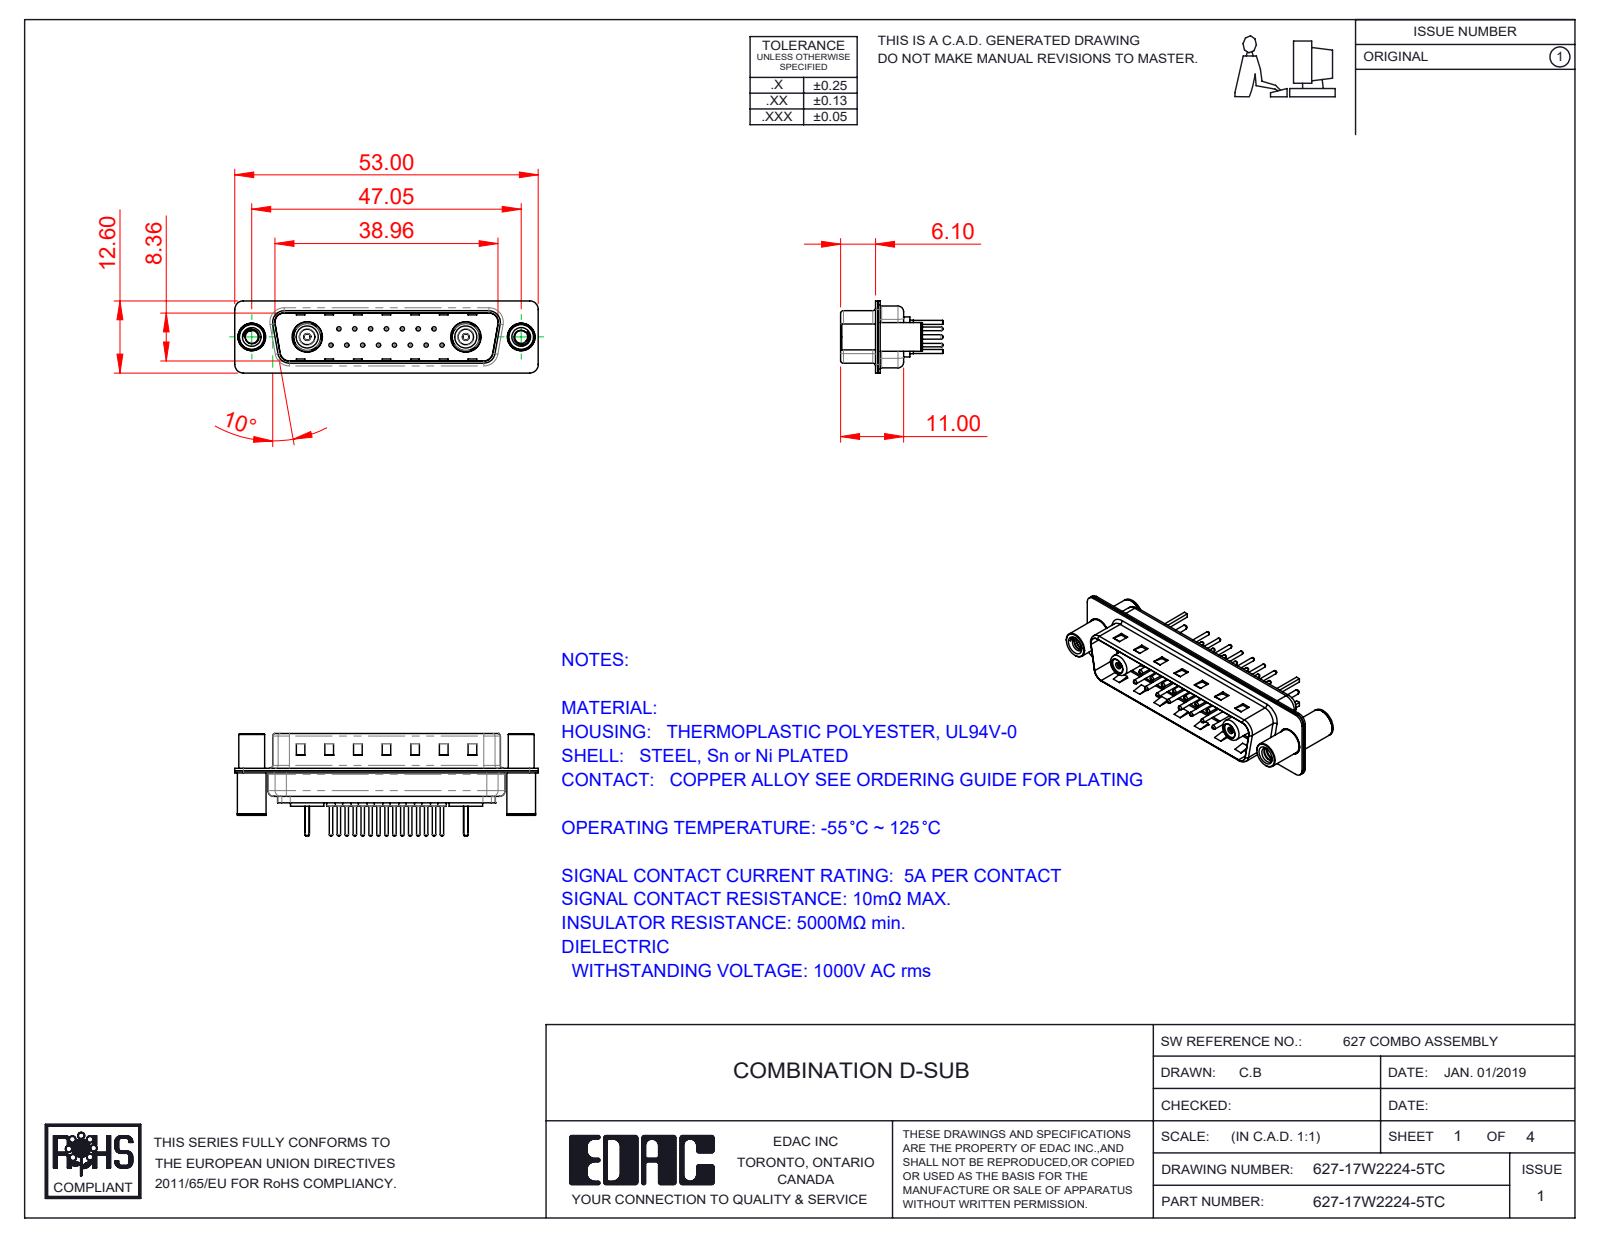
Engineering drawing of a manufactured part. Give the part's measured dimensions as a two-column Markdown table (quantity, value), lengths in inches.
| quantity | value |
| --- | --- |
| part name | 627-17W2224-5TC; Locking Collar; 627Combo Contact Row 2_24; Co-Ax Jack Assy_S (+8 more) |
| STEP written by | SolidWorks 2016 (CONFIG_CONTROL_DESIGN) |
| units | inches |
| bodies | 30 solids, 1248 faces (376 planar, 503 cylindrical, 369 other) |
| overall size | 2.087 × 0.705 × 0.496 |
| volume | 0.186 in³ |
| surface area | 12.59 in² |
| round holes (diameter × count) | 0.063 × 17, 0.03 × 15, 0.079 × 15, 0.043 × 2, 0.047 × 2, 0.059 × 2, 0.089 × 2, 0.098 × 2, 0.106 × 2, 0.128 × 2, 0.134 × 2, 0.157 × 2 |
| round bosses / shafts (diameter × count) | 0.059 × 15, 0.024 × 15, 0.23 × 2, 0.205 × 2, 0.197 × 2, 0.193 × 2, 0.189 × 2, 0.186 × 2 |
| partial cylindrical surfaces (radius × count) | 0.059 × 16, 0.079 × 12, 0.02 × 8, 0.063 × 8, 0.01 × 4, 0.024 × 4, 0.026 × 4, 0.035 × 4 |
| main face-to-face distances | 0.016, 0.032, 0.377, 0.345, 0.236, 0.059, 0.031, 0.22, 0.048, 0.393 |
| hole center spacings | 0.124, 0.109, 0.218, 0.327, 0.198, 0.295, 0.436, 0.198 |
